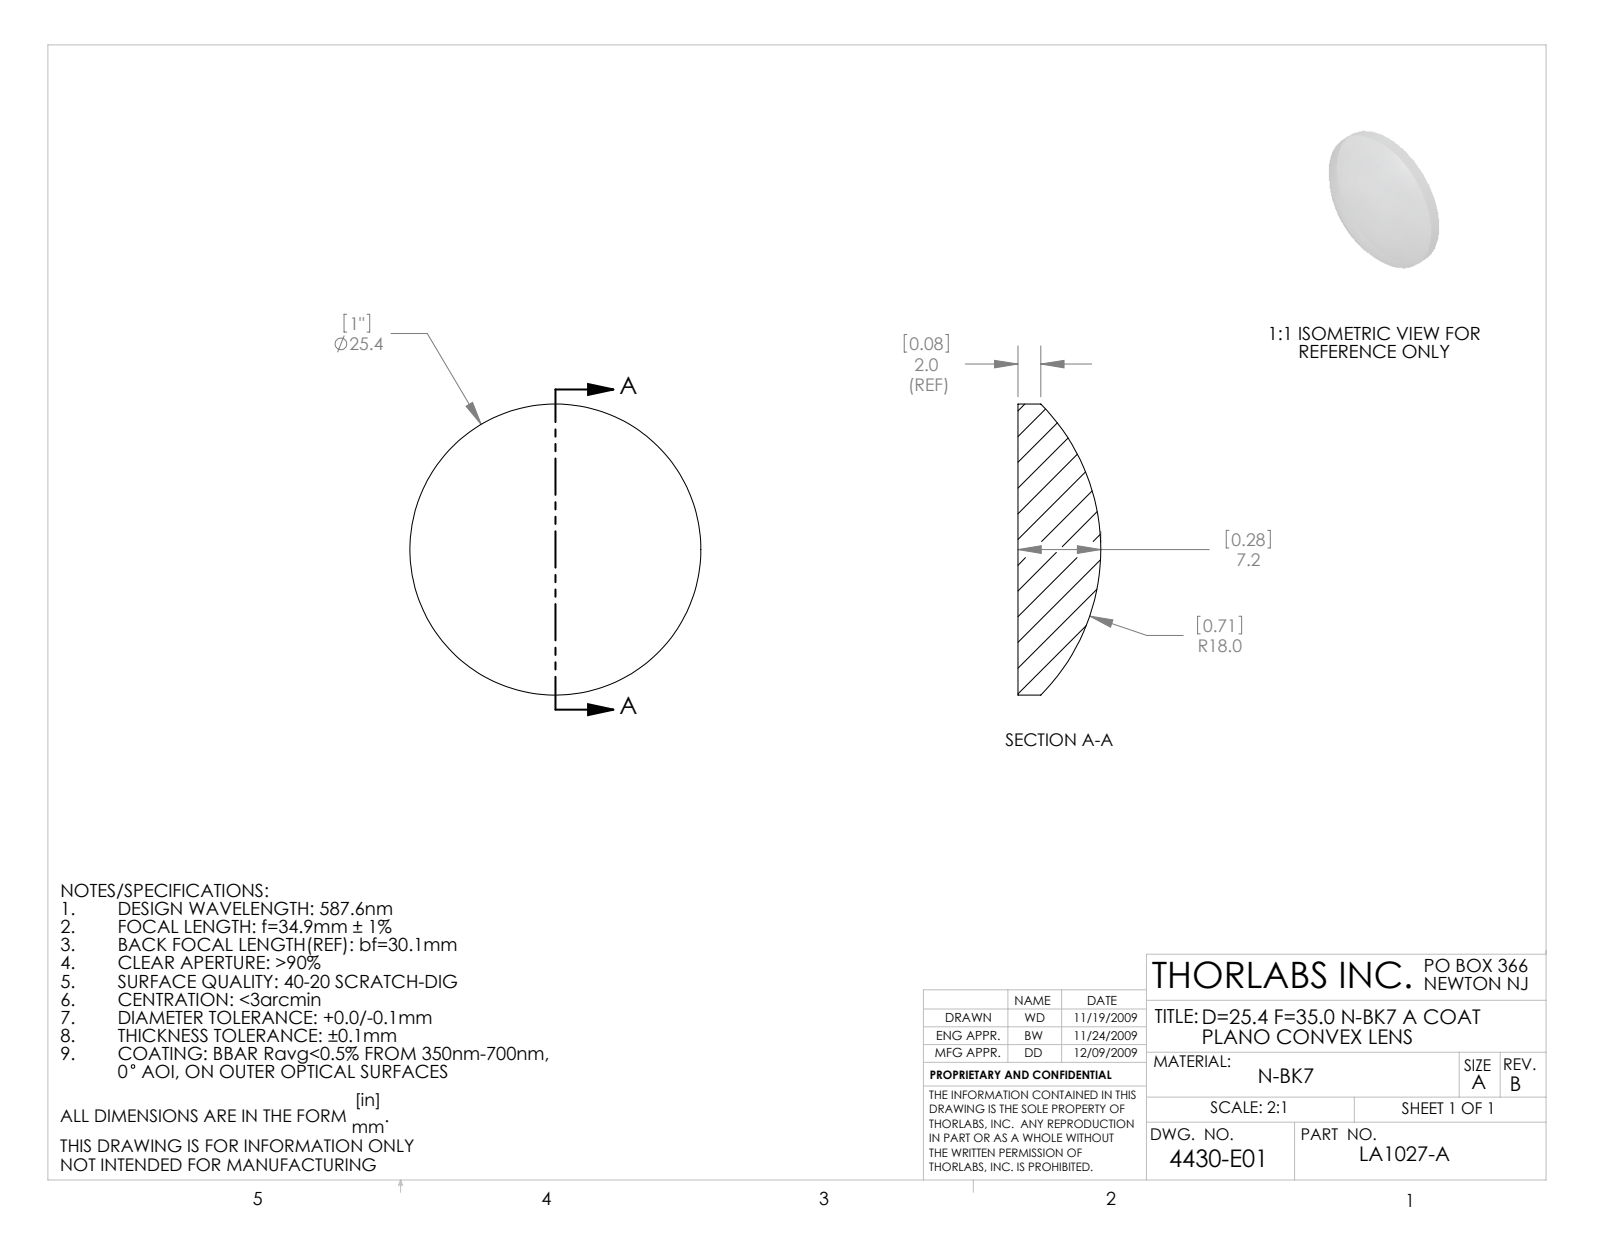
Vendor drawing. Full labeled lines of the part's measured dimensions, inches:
Part name (STEP PRODUCT): 4430-E0W
STEP written by: SolidWorks 2009 (AUTOMOTIVE_DESIGN)
Units: inches
Bodies: 1 solid, 5 faces (1 planar, 2 cylindrical, 2 other)
Overall size (bounding box): 1 × 1 × 0.285
Volume: 0.147 in³ · Surface area: 1.951 in²
Round bosses / shafts (diameter × count): ⌀1 ×1
